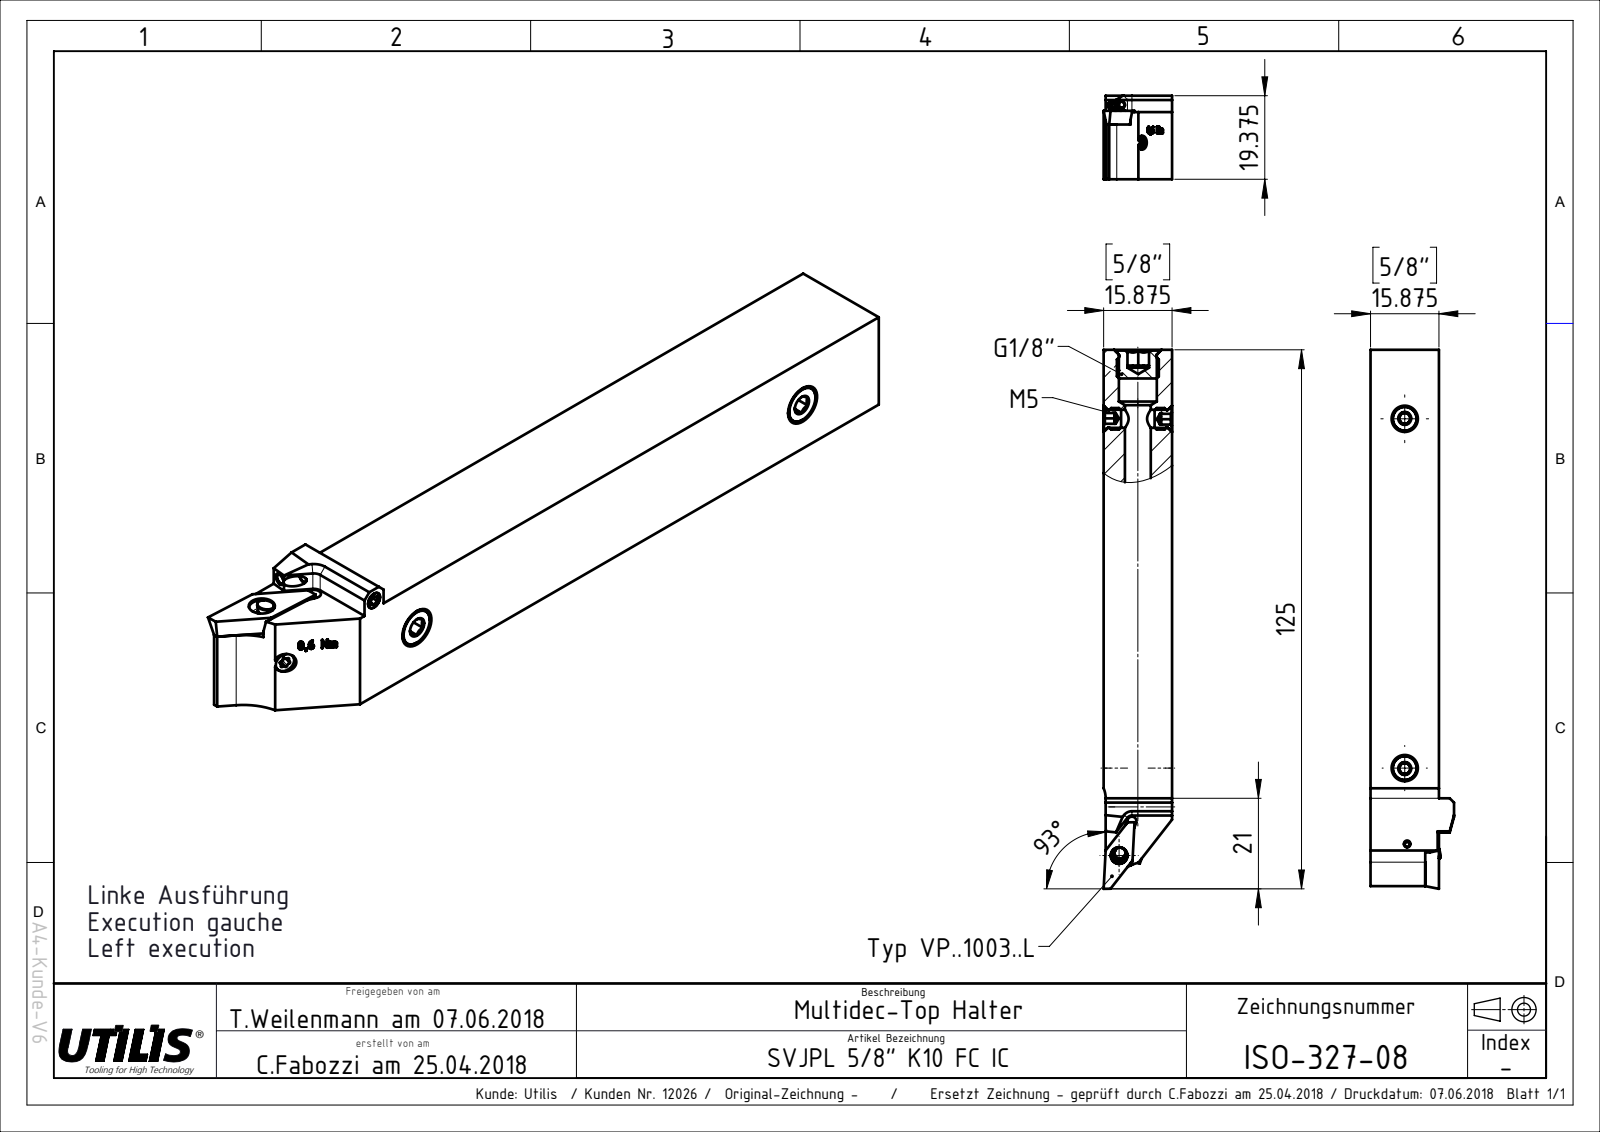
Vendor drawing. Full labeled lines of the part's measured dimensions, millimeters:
Part name (STEP PRODUCT): ISO-327-08
STEP written by: SolidWorks 2017 (AUTOMOTIVE_DESIGN)
Units: millimetres
Bodies: 1 solid, 124 faces (63 planar, 8 cylindrical, 53 other)
Overall size (bounding box): 125 × 19.38 × 15.88
Volume: 29 694 mm³ · Surface area: 8 256 mm²
Round holes (diameter × count): ⌀3.2 ×1
Partial cylindrical surfaces — rounded edges, fillets, slot ends (radius × count): R1.05 ×1, R1.31 ×1, R6 ×1, R6.1 ×1, R8.81 ×1
Main face-to-face distances: 15.88, 0.47, 15.41, 15.58, 104, 19.38, 3.8, 3.5, 2, 4
